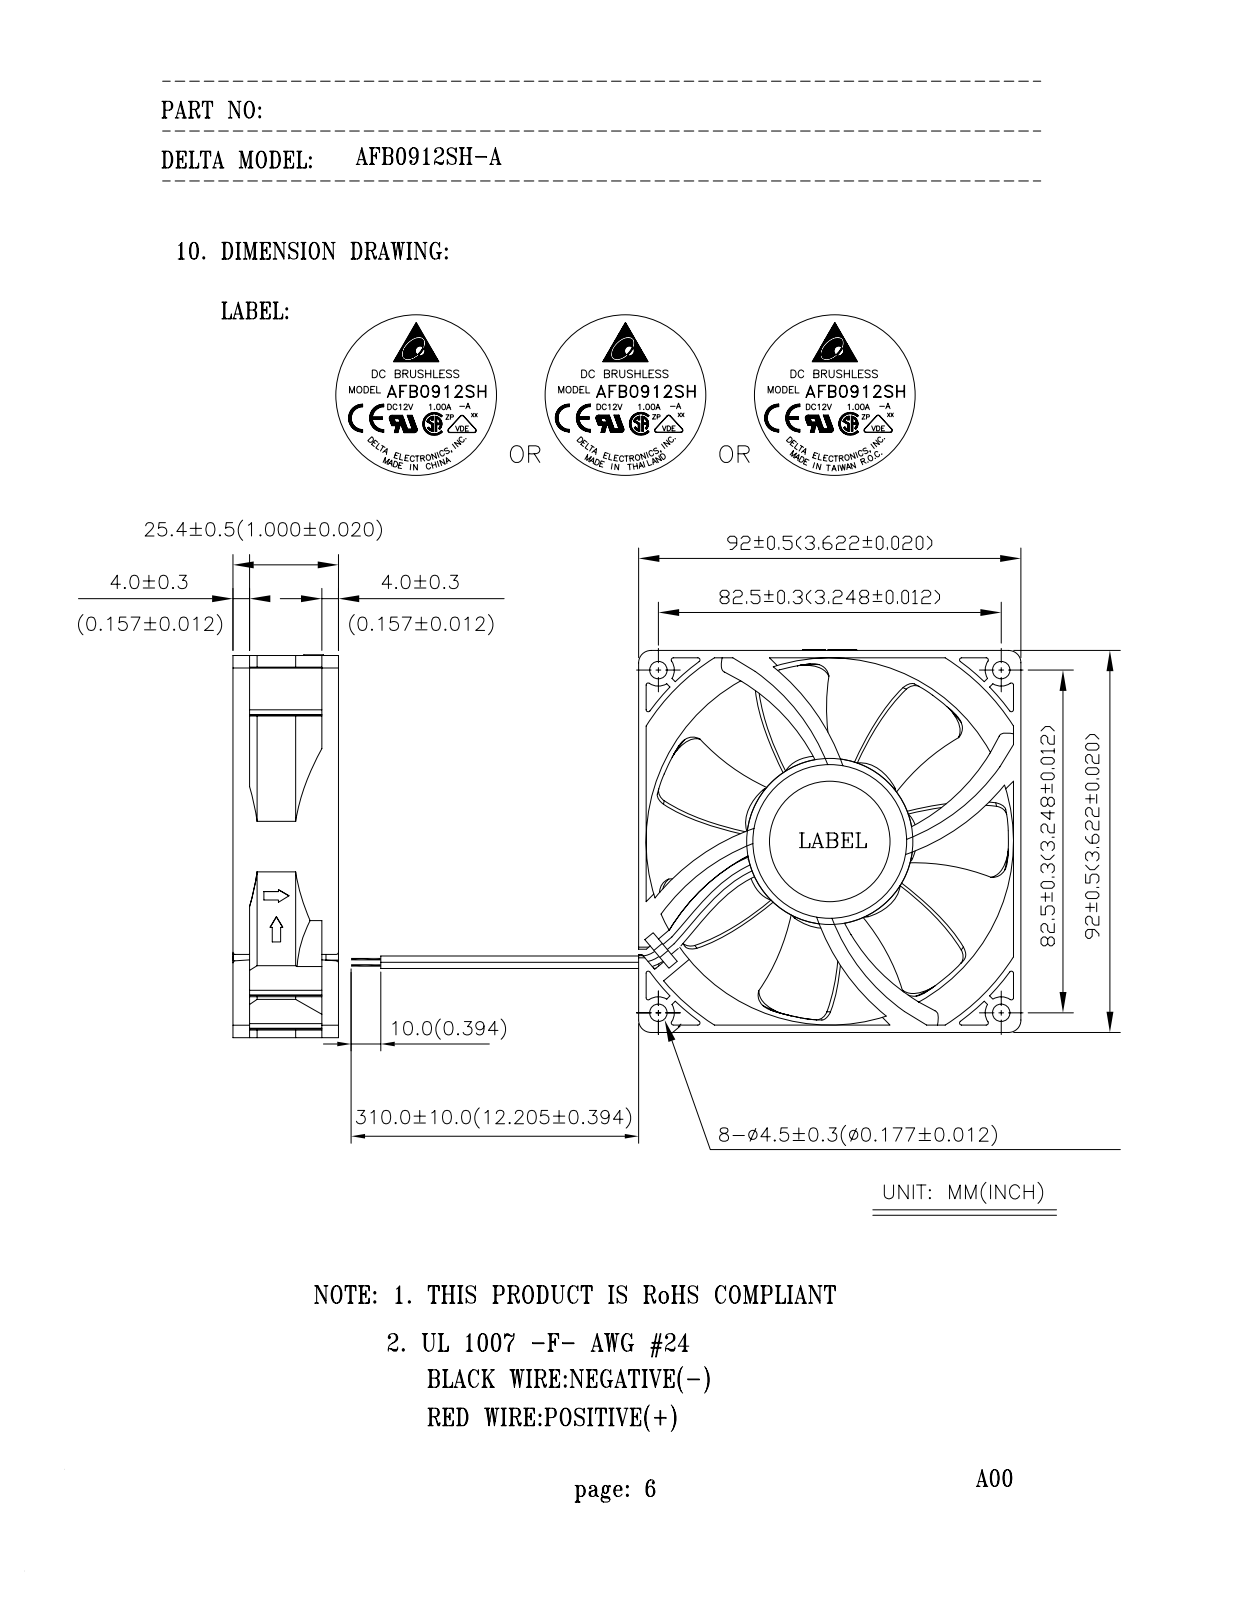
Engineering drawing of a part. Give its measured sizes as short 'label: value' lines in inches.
name: AFC0912D-AF00
written by: CREO PARAMETRIC BY PTC INC, 2015080 (CONFIG_CONTROL_DESIGN)
unit: in
bodies: 1 solid, 618 faces (373 planar, 176 cylindrical, 69 other)
size: 3.63 × 3.622 × 1
volume: 11.55 in³; area: 48.8 in²
holes: 4× ⌀0.165, 1× ⌀0.048
bosses: 1× ⌀3.654
rounds: 32× R0.02, 16× R0.031, 4× R0.016, 4× R0.038, 4× R0.049, 4× R0.069, 4× R0.08, 4× R0.118
face distances: 1, 3.622, 0.843, 0.157, 0.079, 0.071, 0.685, 0.921, 0.764, 4.156
hole spacings: 3.248, 4.593
